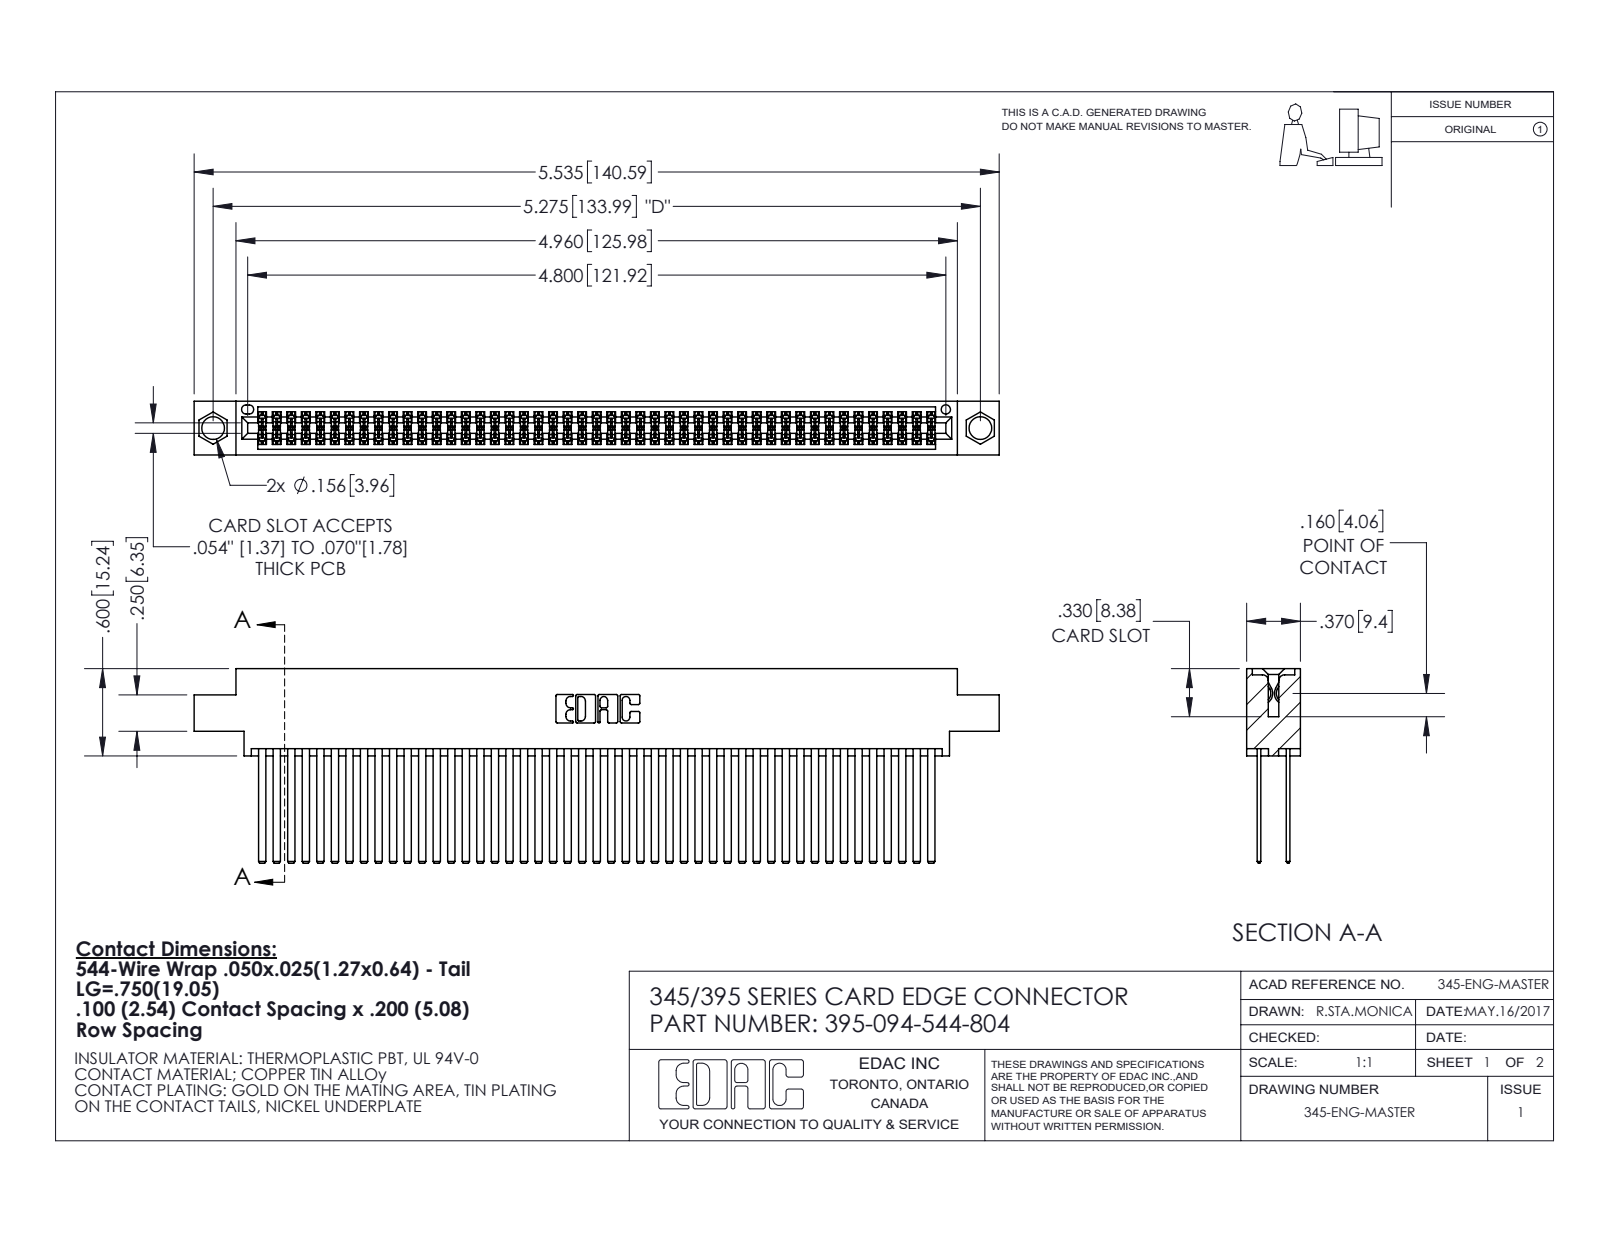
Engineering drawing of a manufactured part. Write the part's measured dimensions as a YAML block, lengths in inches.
part_name: "395-094-544-804; 345-292-001_345-293-144; 345 Part_0.170 Offset - 0.156 Dia-TI"
step_written_by: "SolidWorks 2020 (CONFIG_CONTROL_DESIGN)"
units: inches
bodies: {solids: 95, faces: 4280, planar: 2824, cylindrical: 1456, other: 0}
overall_size: [5.535, 1.337, 0.37]
volume: 0.903
surface_area: 40.04
round_holes:
  - {diameter: 0.156, count: 2}
  - {diameter: 0.064, count: 1}
partial_cylinders:
  - {radius: 0.006, count: 141}
  - {radius: 0.01, count: 22}
  - {radius: 0.007, count: 6}
  - {radius: 0.031, count: 6}
  - {radius: 0.026, count: 3}
  - {radius: 0.014, count: 2}
  - {radius: 0.019, count: 2}
  - {radius: 0.022, count: 2}
face_to_face_distances: [0.2, 0.025, 0.072, 0.098, 0.272, 0.298, 0.225, 0.175, 0.37, 0.15]
hole_center_spacings: [0.27, 5.039, 5.275]
